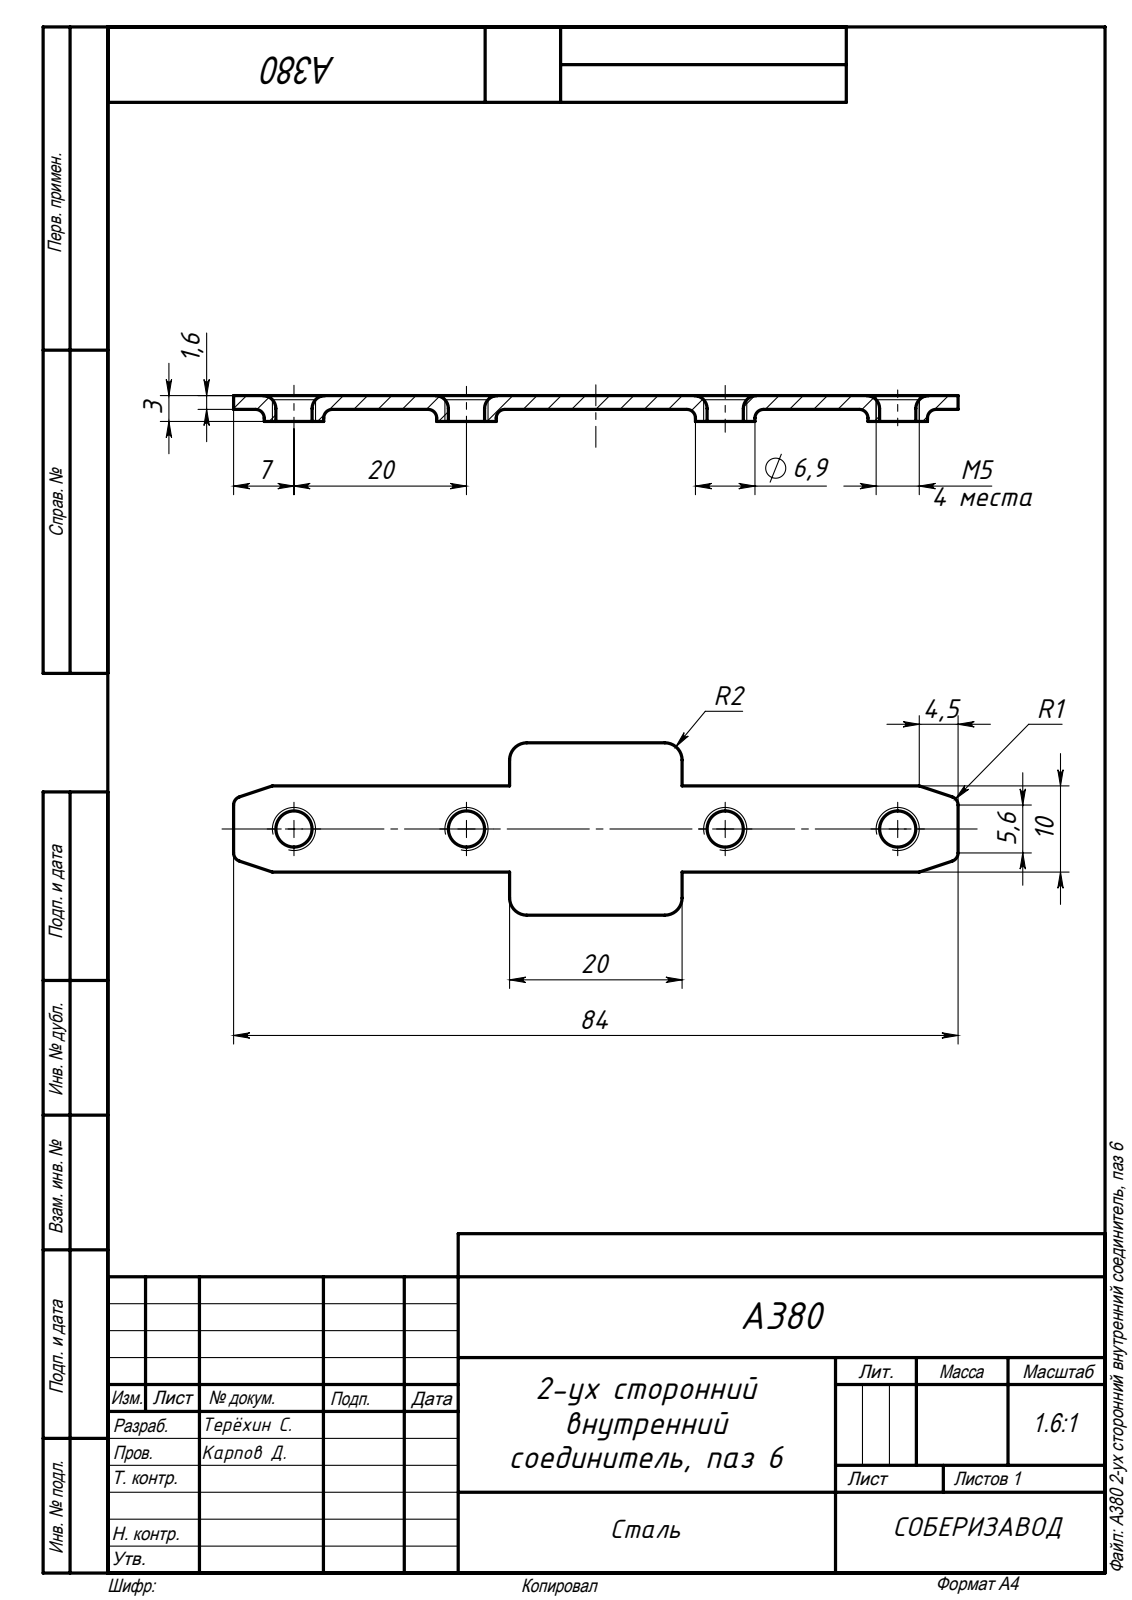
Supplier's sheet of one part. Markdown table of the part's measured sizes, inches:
| quantity | value |
| --- | --- |
| part name | A380 2-ух сторонний внутренний соединитель, паз 6 |
| STEP written by | SolidWorks 2020 (AUTOMOTIVE_DESIGN) |
| units | inches |
| bodies | 1 solid, 62 faces (22 planar, 24 cylindrical, 16 other) |
| overall size | 3.307 × 0.787 × 0.118 |
| volume | 0.102 in³ |
| surface area | 3.824 in² |
| round holes (diameter × count) | 0.165 × 4 |
| round bosses / shafts (diameter × count) | 0.272 × 4 |
| partial cylindrical surfaces (radius × count) | 0.039 × 4, 0.079 × 4 |
| main face-to-face distances | 0.063, 0.055, 0.118, 0.394, 0.197, 0.591, 0.787, 1.26, 2.047, 1.306 |
| hole center spacings | 0.787, 1.969, 1.181, 2.756 |
